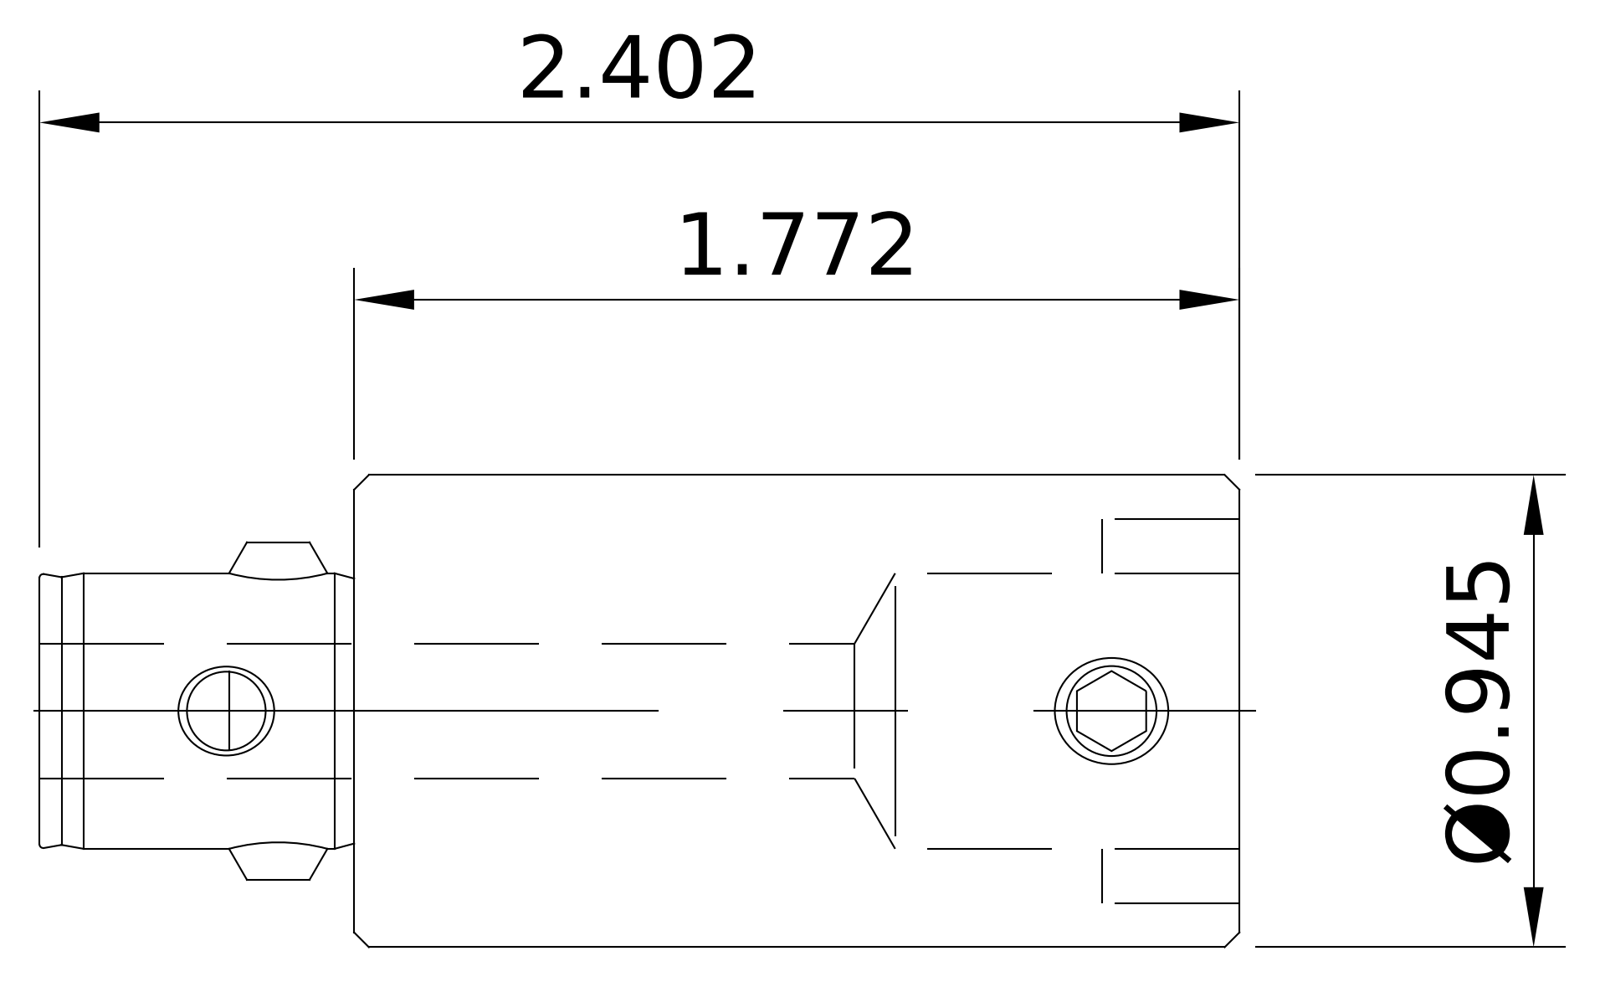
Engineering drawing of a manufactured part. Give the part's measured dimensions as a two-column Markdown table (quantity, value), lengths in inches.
| quantity | value |
| --- | --- |
| part name | 11.331.221; 10.691.50X_10.691.502; 691-50XRing_10.691.502Ring; 10.690.43X_10.690.432 (+1 more) |
| STEP written by | SolidWorks 2015 (AUTOMOTIVE_DESIGN) |
| units | inches |
| bodies | 4 solids, 122 faces (35 planar, 40 cylindrical, 47 other) |
| overall size | 2.402 × 0.945 × 0.945 |
| volume | 1.11 in³ |
| surface area | 11.18 in² |
| round holes (diameter × count) | 0.138 × 1, 0.157 × 1, 0.165 × 1, 0.197 × 1, 0.205 × 1, 0.276 × 1, 0.551 × 1, 0.571 × 1 |
| round bosses / shafts (diameter × count) | 0.945 × 1, 0.197 × 1, 0.193 × 1, 0.126 × 1 |
| partial cylindrical surfaces (radius × count) | 0.079 × 2, 0.276 × 1 |
| main face-to-face distances | 1.772, 0.63, 2.402, 0.464, 2.13, 1.5, 0.272, 0.039, 0.128, 0.122 |
| hole center spacings | 1.76 |
